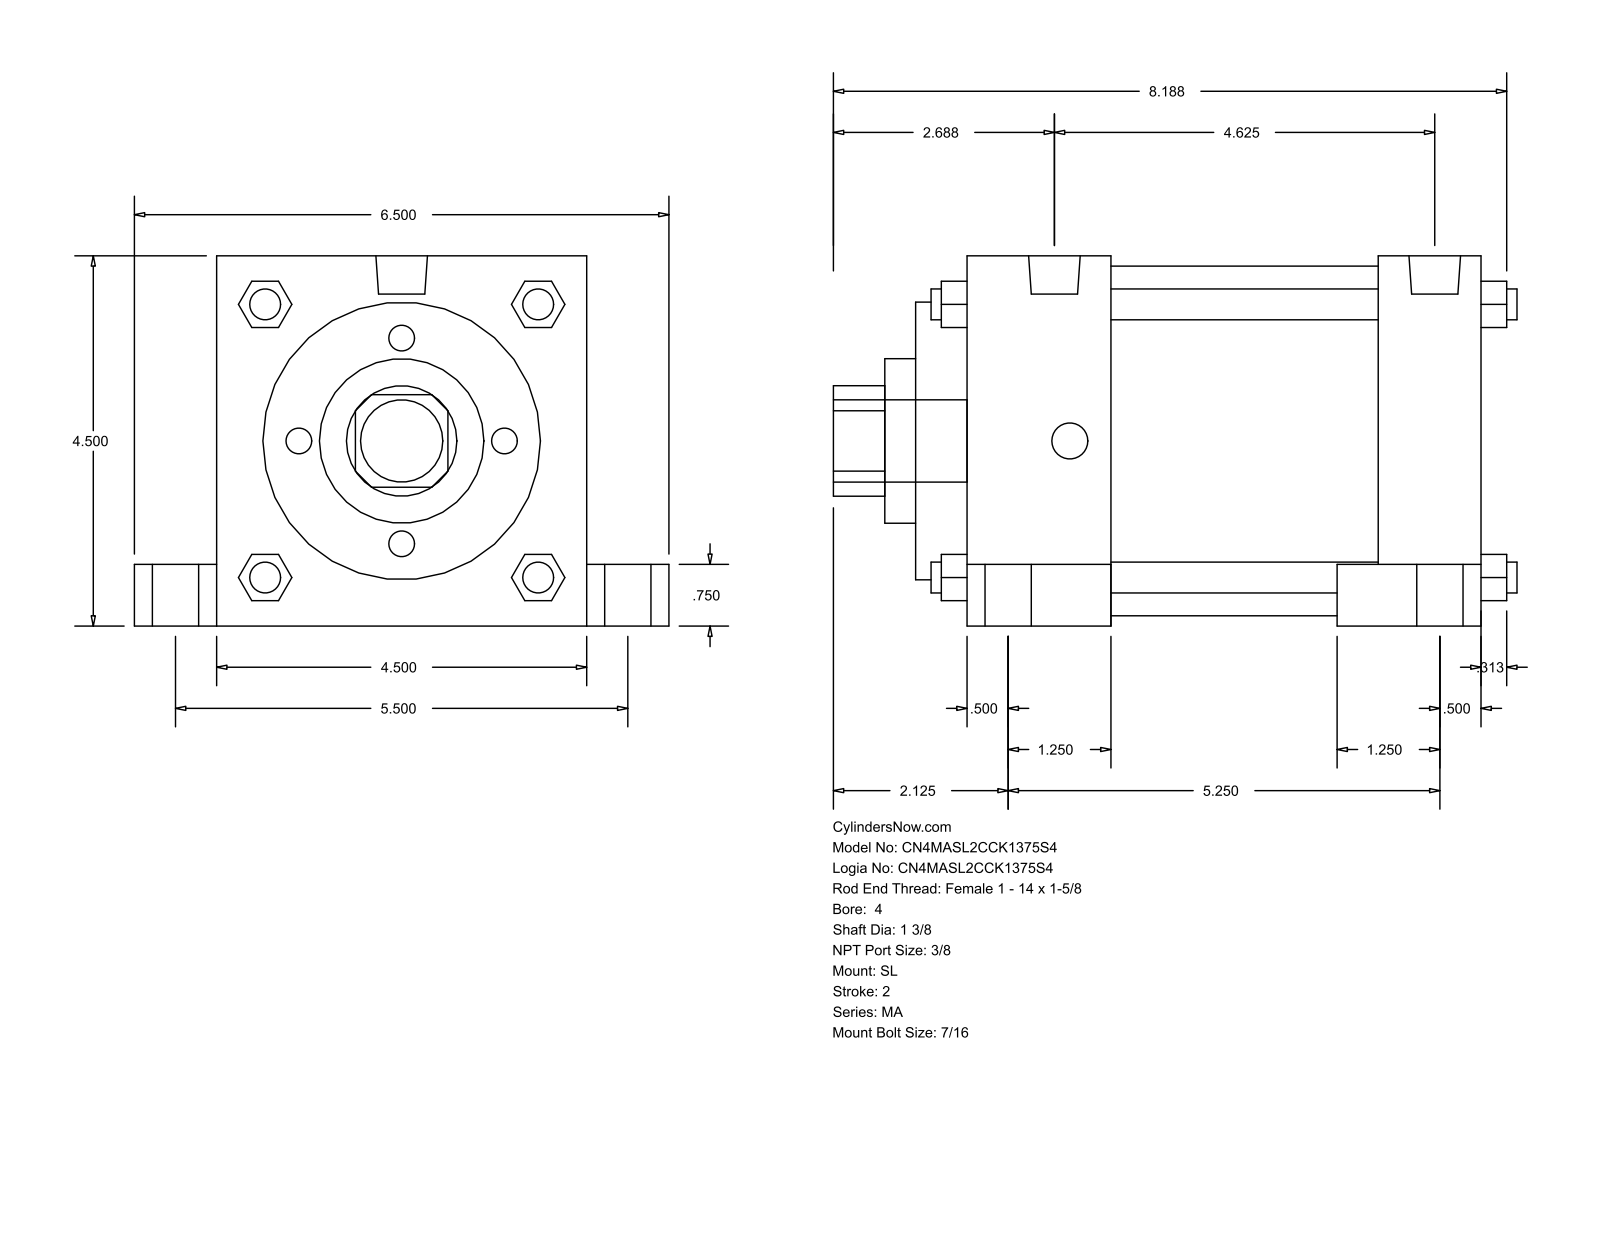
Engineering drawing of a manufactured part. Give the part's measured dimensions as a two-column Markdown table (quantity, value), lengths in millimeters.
| quantity | value |
| --- | --- |
| part name | MA_SL__0400_1.375 |
| STEP written by | GSSL Pune (CONFIG_CONTROL_DESIGN) |
| units | millimeters |
| bodies | 0 solids, 150 faces (113 planar, 37 cylindrical, 0 other) |
| overall size | 211.14 × 165.1 × 114.3 |
| round holes (diameter × count) | 34.92 × 1, 50.8 × 1, 85.72 × 1, 107.95 × 1 |
| round bosses / shafts (diameter × count) | 20.64 × 4, 14.29 × 4, 11.11 × 4, 9.53 × 4, 15.93 × 2, 25.4 × 1 |
| partial cylindrical surfaces (radius × count) | 17.06 × 1 |
| main face-to-face distances | 114.3, 158.76, 15.87, 174.63, 60.32, 44.45, 114.31, 142.88, 127.01, 82.56 |
